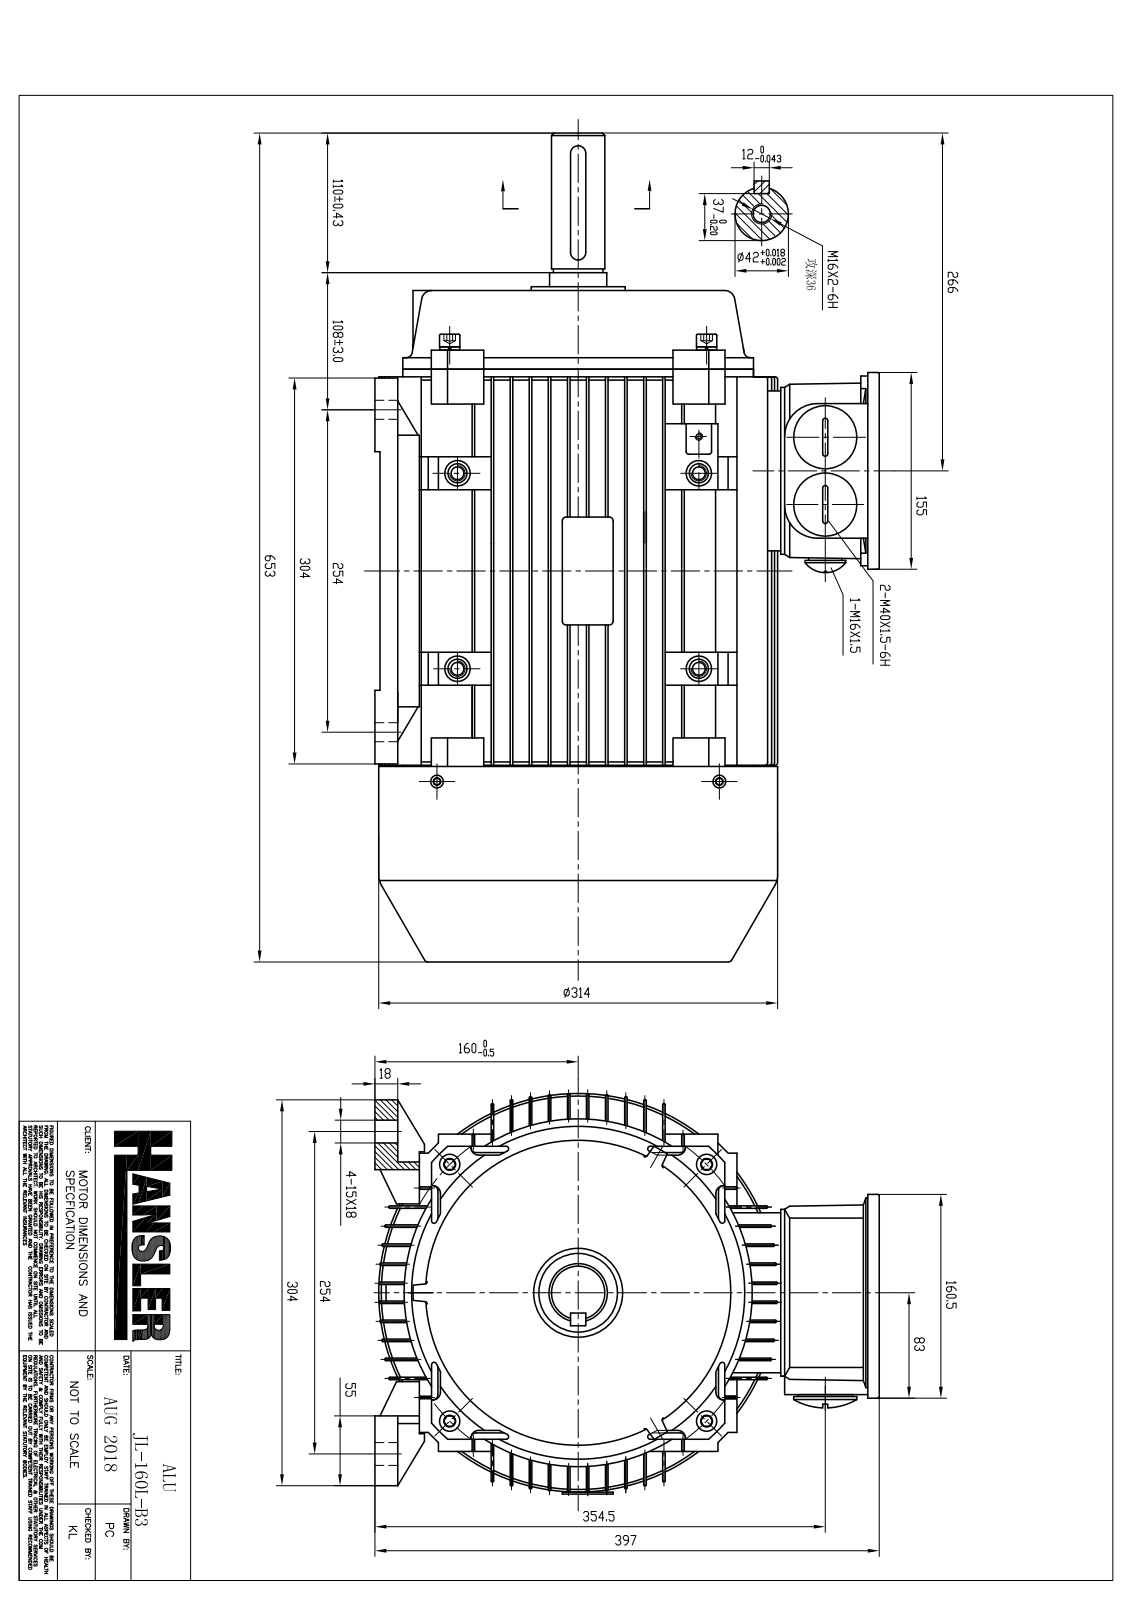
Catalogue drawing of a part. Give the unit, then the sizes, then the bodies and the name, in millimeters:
Units: millimetres
Overall size (bounding box): 650.92 × 402.7 × 316
Round holes (diameter × count): ⌀5 ×28, ⌀4.12 ×12, ⌀8.39 ×8, ⌀9.1 ×8, ⌀10 ×8, ⌀21 ×8, ⌀5.25 ×5, ⌀5.3 ×5, ⌀8 ×5, ⌀16 ×5, ⌀4.2 ×4, ⌀5.48 ×4
Round bosses / shafts (diameter × count): ⌀8 ×10, ⌀5.38 ×9, ⌀15 ×8, ⌀12.59 ×8, ⌀7.19 ×8, ⌀10 ×5, ⌀7.85 ×5, ⌀4.48 ×5
Partial cylindrical surfaces — rounded edges, fillets, slot ends (radius × count): R1.2 ×302, R1 ×193, R2 ×182, R4 ×40, R1.37 ×37, R3 ×32, R1.5 ×26, R3.42 ×25
Main face-to-face distances: 15, 30, 2, 45, 13, 90, 17, 75, 60, 105
Hole centre spacings: 202.36, 14.64, 202.24, 95.35, 134, 202.23, 78, 110
Volume: 7 181 000 mm³ · Surface area: 2 817 000 mm²
Bodies: 67 solids, 8950 faces (4029 planar, 2224 cylindrical, 2697 other)
Part name (STEP PRODUCT): JL-160L-B3
STEP written by: SIEMENS PLM Software NX 12.0 (AP203_CONFIGURATION_CONTROLLED_3D_DESIGN_OF_MECHANICAL_PARTS_AND_ASSEMBLIES_MIM_LF)
